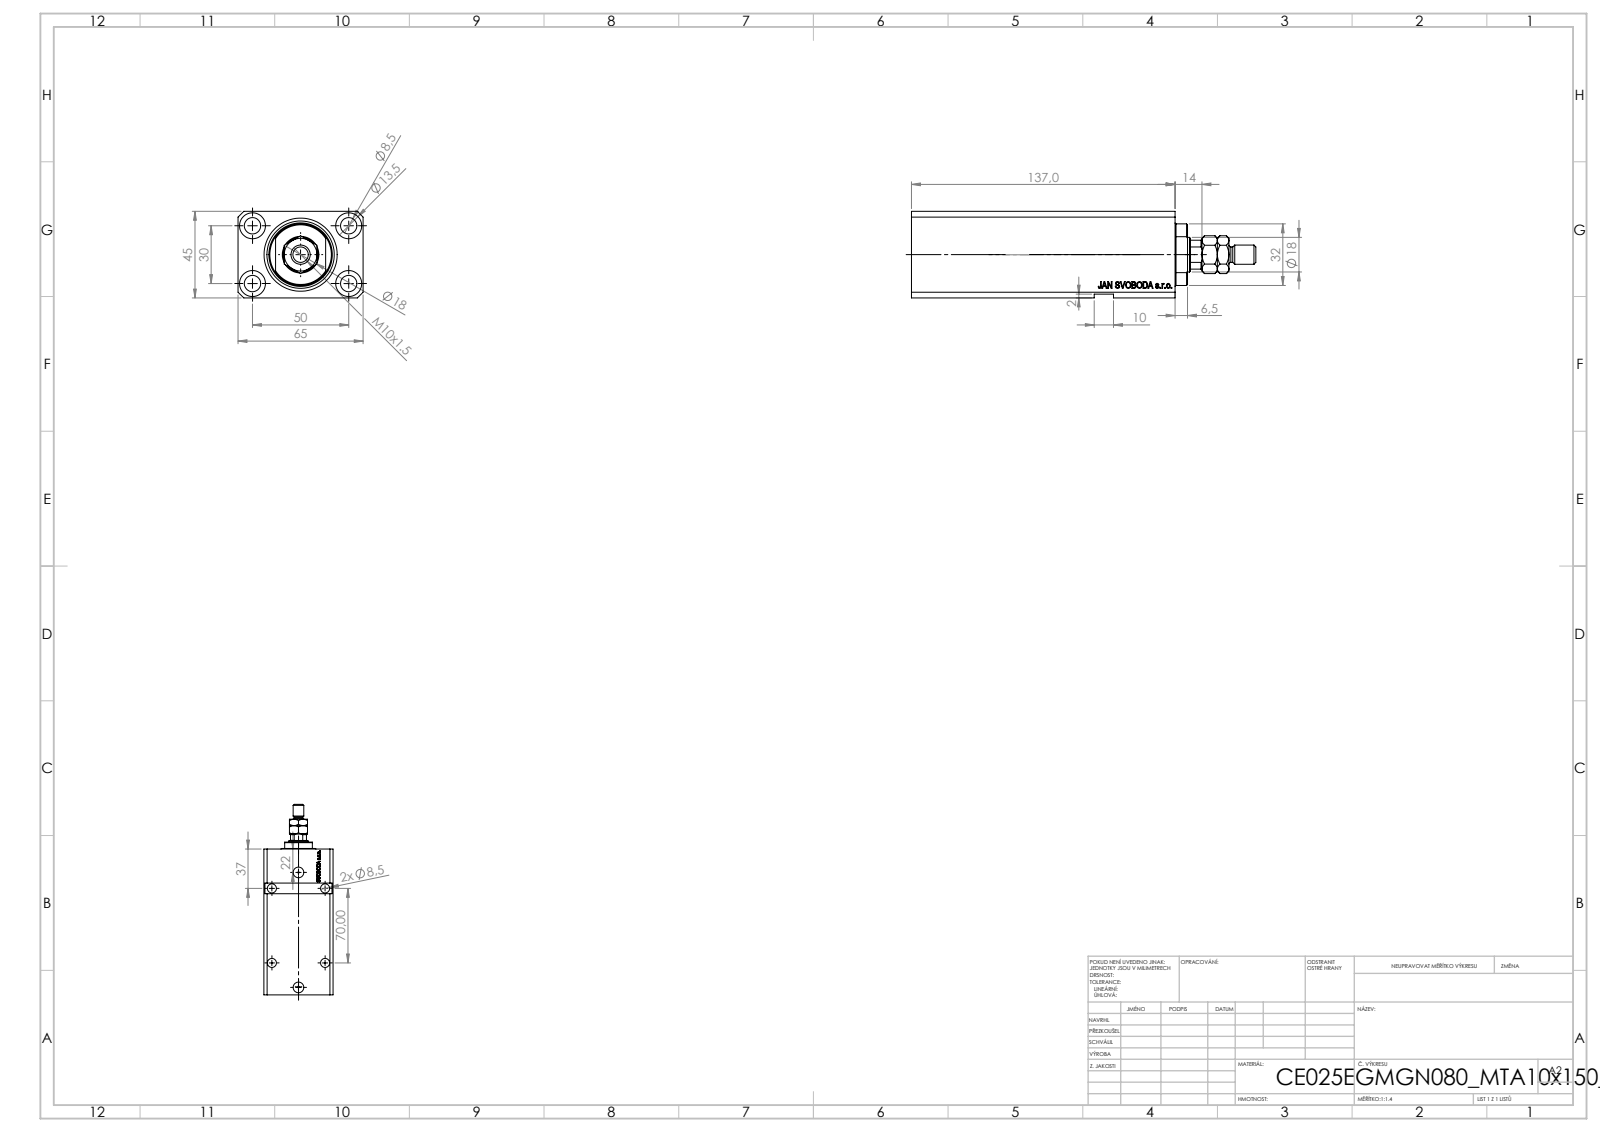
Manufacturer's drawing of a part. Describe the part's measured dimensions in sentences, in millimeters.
The part is named "MTA; V250CE_VC_E; V250CE_C_VCP; V250CE_E_Body". Its 3-D file was written by "SolidWorks 2019 (CONFIG_CONTROL_DESIGN)". It is 4 solids with 966 faces: 450 planar, 108 cylindrical and 408 other. Overall it measures 179 by 65 by 45 millimeters. Its volume is 339 348 cubic millimeters and its surface area 82 310 square millimeters. Round holes: 9 of diameter 8.5, 4 of diameter 1.25, 4 of diameter 13.5, 2 of diameter 10, 2 of diameter 13.16, 2 of diameter 20, 1 of diameter 18, 1 of diameter 25, 1 of diameter 38. Round bosses or shafts: 1 of diameter 10, 1 of diameter 8. Partial cylindrical surfaces (rounded edges, fillets, slot ends): 1 of radius 8.5, 1 of radius 16. The main face-to-face distances are 45, 65, 14, 123, 137, 6.9, 116.1, 130.1, 43, 28. The hole center spacings are 29.15, 50, 30, 33.61, 33.97, 58.31, 70, 86.02.
